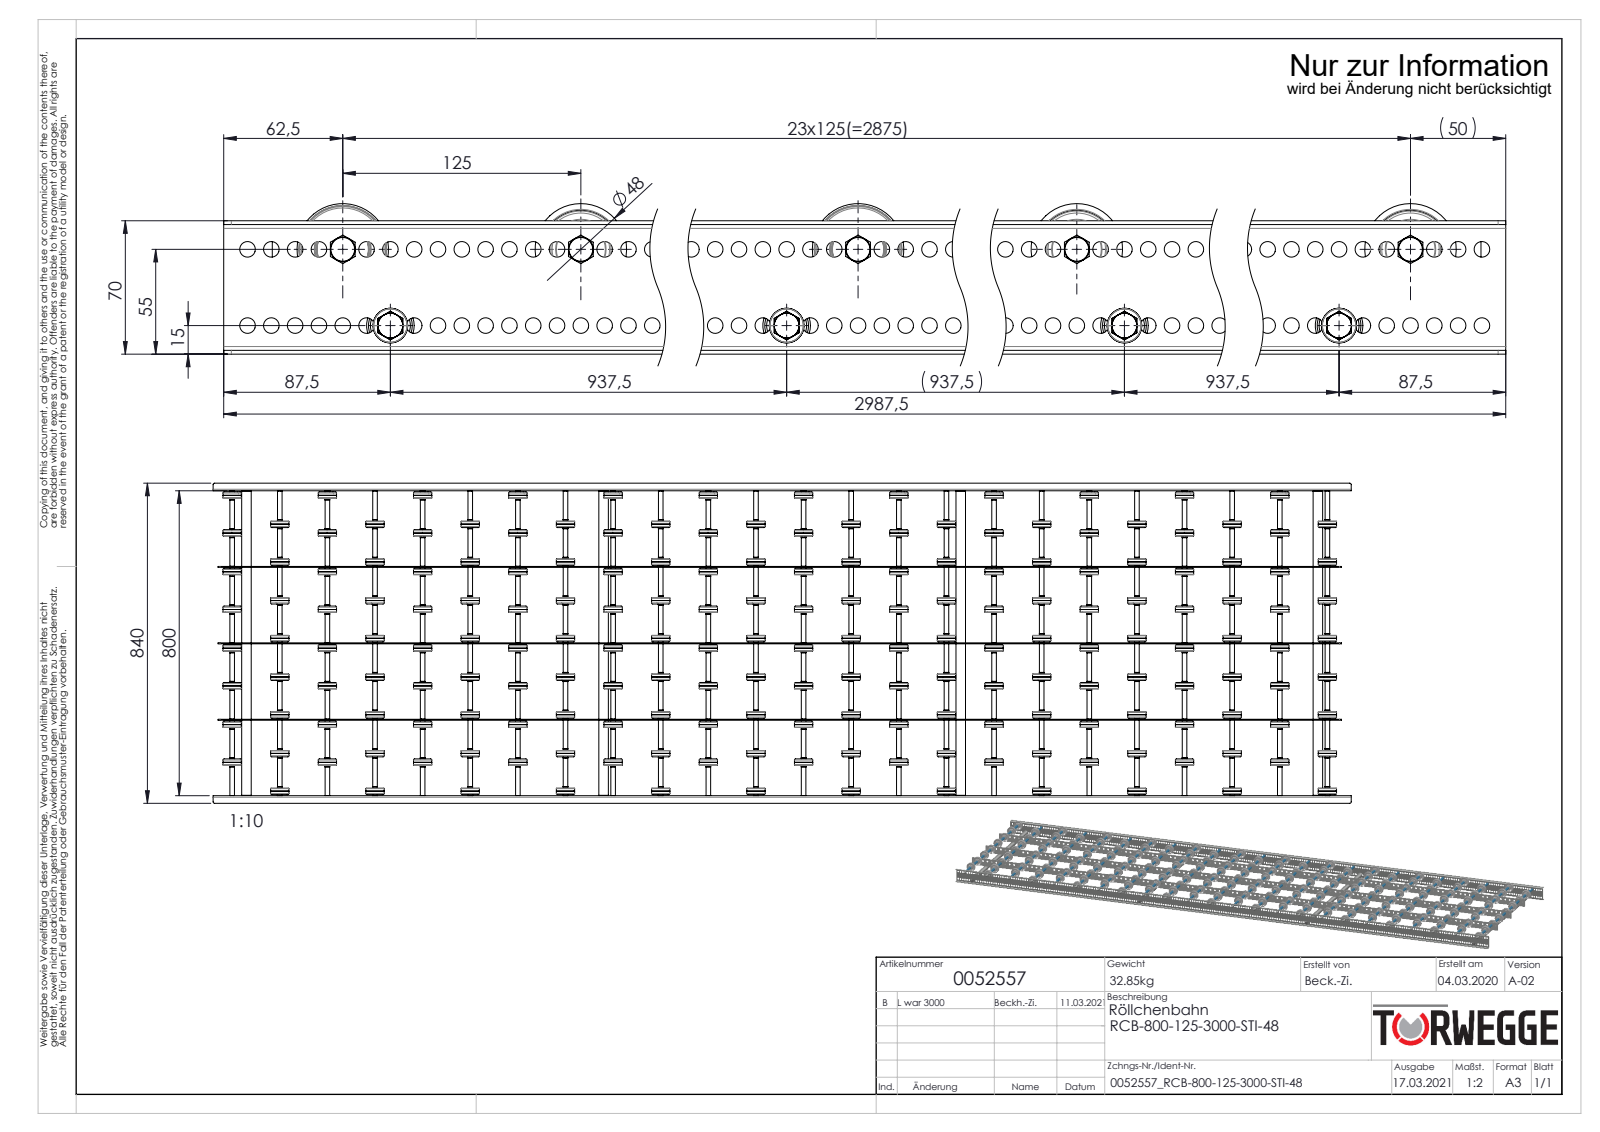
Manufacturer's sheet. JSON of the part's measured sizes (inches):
{"part_name": "Röllchenachse-für-Konfiguration_EL800 Stahl; Profil_LRB-20x70x20x2_KFG_S109080_U-PROFIL-20-70-20-2-LRB-L=2987,5; Hutmutter_DIN_1587_M8; 0046278_KB-ROHR-12X1,75mm_KFG_L75 (+6 more)", "step_written_by": "SolidWorks 2020 (AUTOMOTIVE_DESIGN)", "units": "inches", "bodies": {"solids": 673, "faces": 21198, "planar": 4110, "cylindrical": 8720, "other": 8368}, "overall_size": [117.618, 33.071, 3.11], "volume_in3": 498.2, "surface_area_in2": 9850, "round_holes": [[0.323, 476], [0.335, 118], [0.262, 24], [0.315, 24], [0.38, 24], [0.591, 24], [1.614, 24], [0.268, 4], [0.827, 4]], "round_bosses_or_shafts": [[1.89, 24], [0.512, 24], [0.492, 24], [0.488, 24], [0.472, 24], [0.453, 24], [0.984, 4], [0.315, 4]], "partial_cylinders_radius": [[0.157, 8], [0.079, 4], [0.197, 4]], "face_to_face_distances": [7.894, 15.787, 0.079, 7.992, 0.098, 7.795, 31.575, 23.681, 15.886, 15.689], "hole_center_spacings": [0.492, 0.984, 1.476, 1.969, 2.461, 2.953, 3.445, 3.937]}
